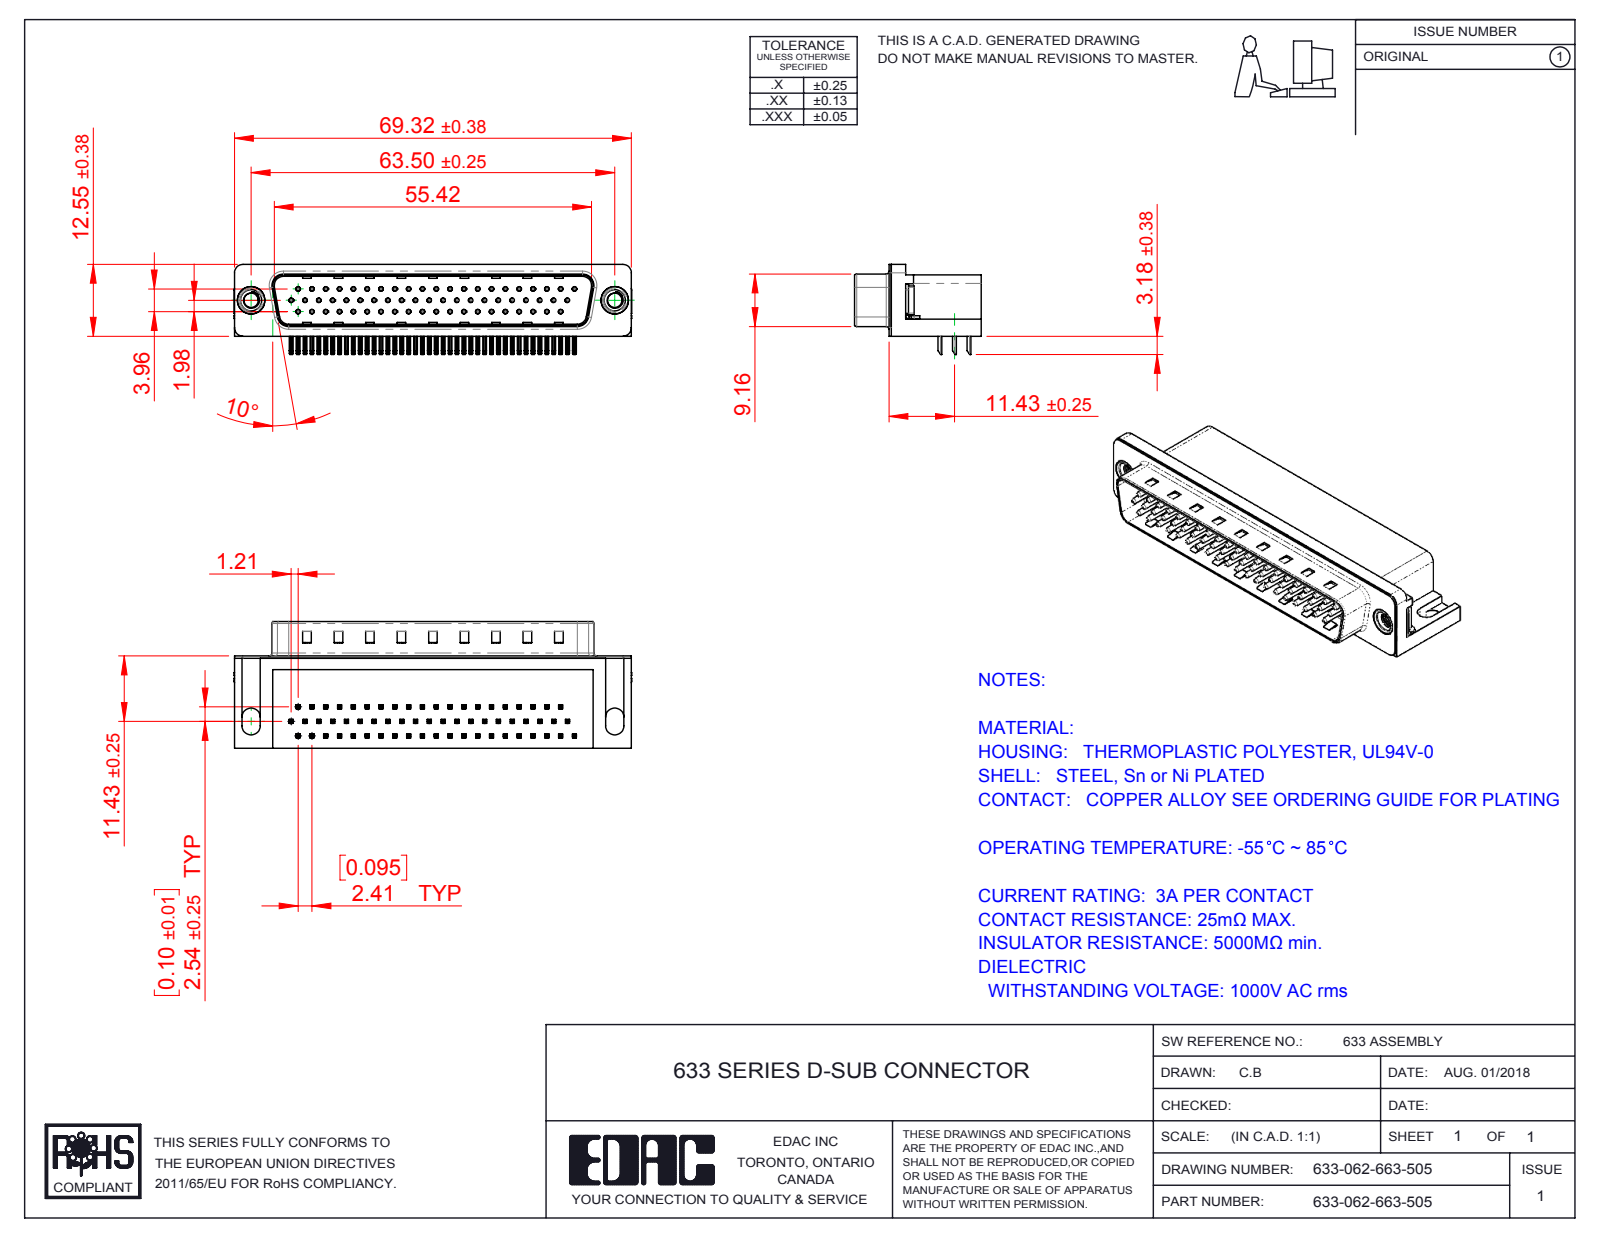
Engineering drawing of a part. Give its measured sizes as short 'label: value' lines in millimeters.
name: 633-062-663-505; 633 M3 Threaded Rivet; 633 Housing_62 Contact; 633 Shell_62 Contact (+4 more)
written by: SolidWorks 2016 (CONFIG_CONTROL_DESIGN)
unit: mm
bodies: 68 solids, 5072 faces (3213 planar, 1442 cylindrical, 417 other)
size: 69.4 × 22.1 × 15.73
volume: 11 002 mm³; area: 13 185 mm²
holes: 62× ⌀0.35, 62× ⌀0.8, 2× ⌀2.5, 2× ⌀4, 2× ⌀4.8, 2× ⌀5
bosses: 62× ⌀0.75, 2× ⌀4.9, 2× ⌀4.75, 2× ⌀3.9
rounds: 256× R0.25, 124× R0.12, 16× R1, 9× R0.5, 8× R1.6, 7× R1.5, 4× R0.9, 4× R2
face distances: 0.4, 10.35, 15.7, 8.76, 2.5, 2.54, 2.9, 8.36, 2.1, 8.6
hole spacings: 2.41, 4.82, 7.24, 9.65, 14.48, 16.89, 4.83, 7.23
